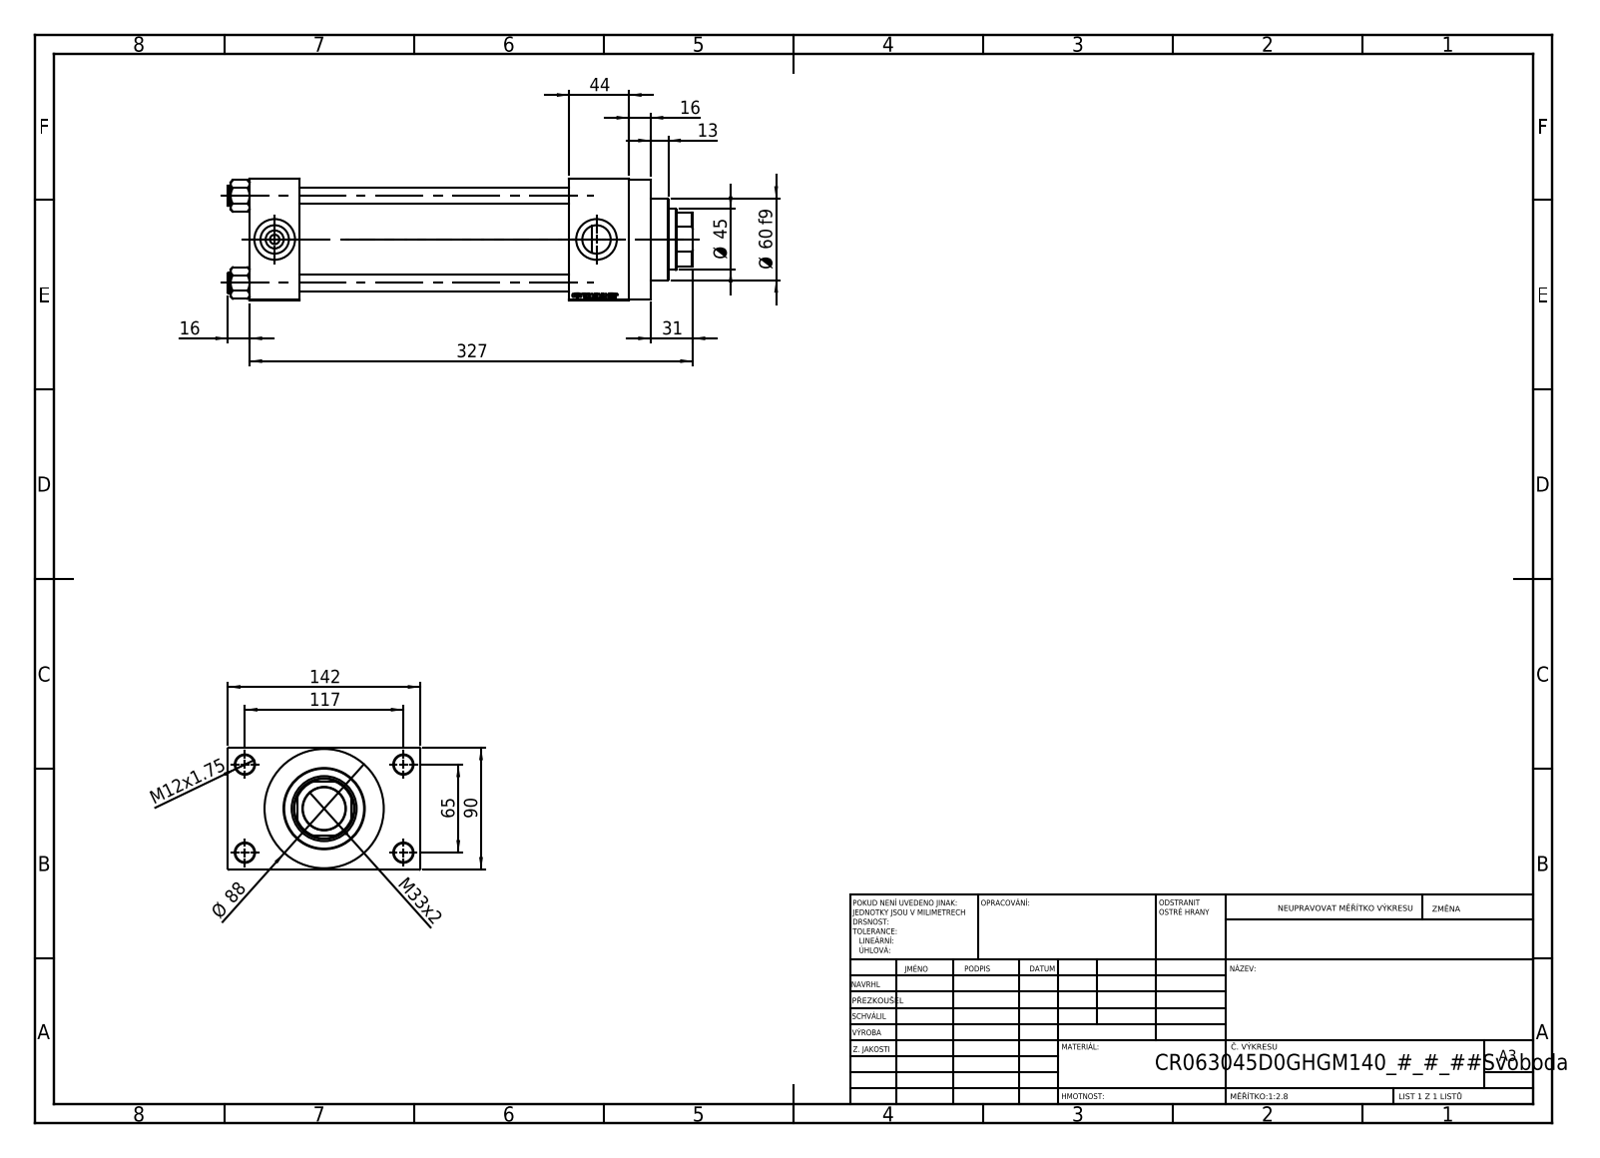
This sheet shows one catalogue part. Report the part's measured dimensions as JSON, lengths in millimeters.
{"part_name": "V215CR_D_Body; V215CR_VCP_D; V215_VC_A; NUT_M5_D (+1 more)", "step_written_by": "SolidWorks 2019 (CONFIG_CONTROL_DESIGN)", "units": "millimeters", "bodies": {"solids": 11, "faces": 1100, "planar": 496, "cylindrical": 86, "other": 518}, "overall_size": [343, 142, 90], "volume_mm3": 1533000, "surface_area_mm2": 311506, "round_holes": [[12, 4], [14, 4], [7, 2], [20.96, 2], [30, 2], [31.5, 1], [45, 1], [48, 1], [50, 1], [60, 1], [63, 1]], "round_bosses_or_shafts": [[15, 4], [88, 1], [69, 1]], "partial_cylinders_radius": [[22, 1]], "face_to_face_distances": [90, 199, 37, 236, 26, 280, 243, 44, 116, 60], "hole_center_spacings": [26.35, 45.47, 64.3, 66.92, 69.81, 90.65, 111.34, 65]}
